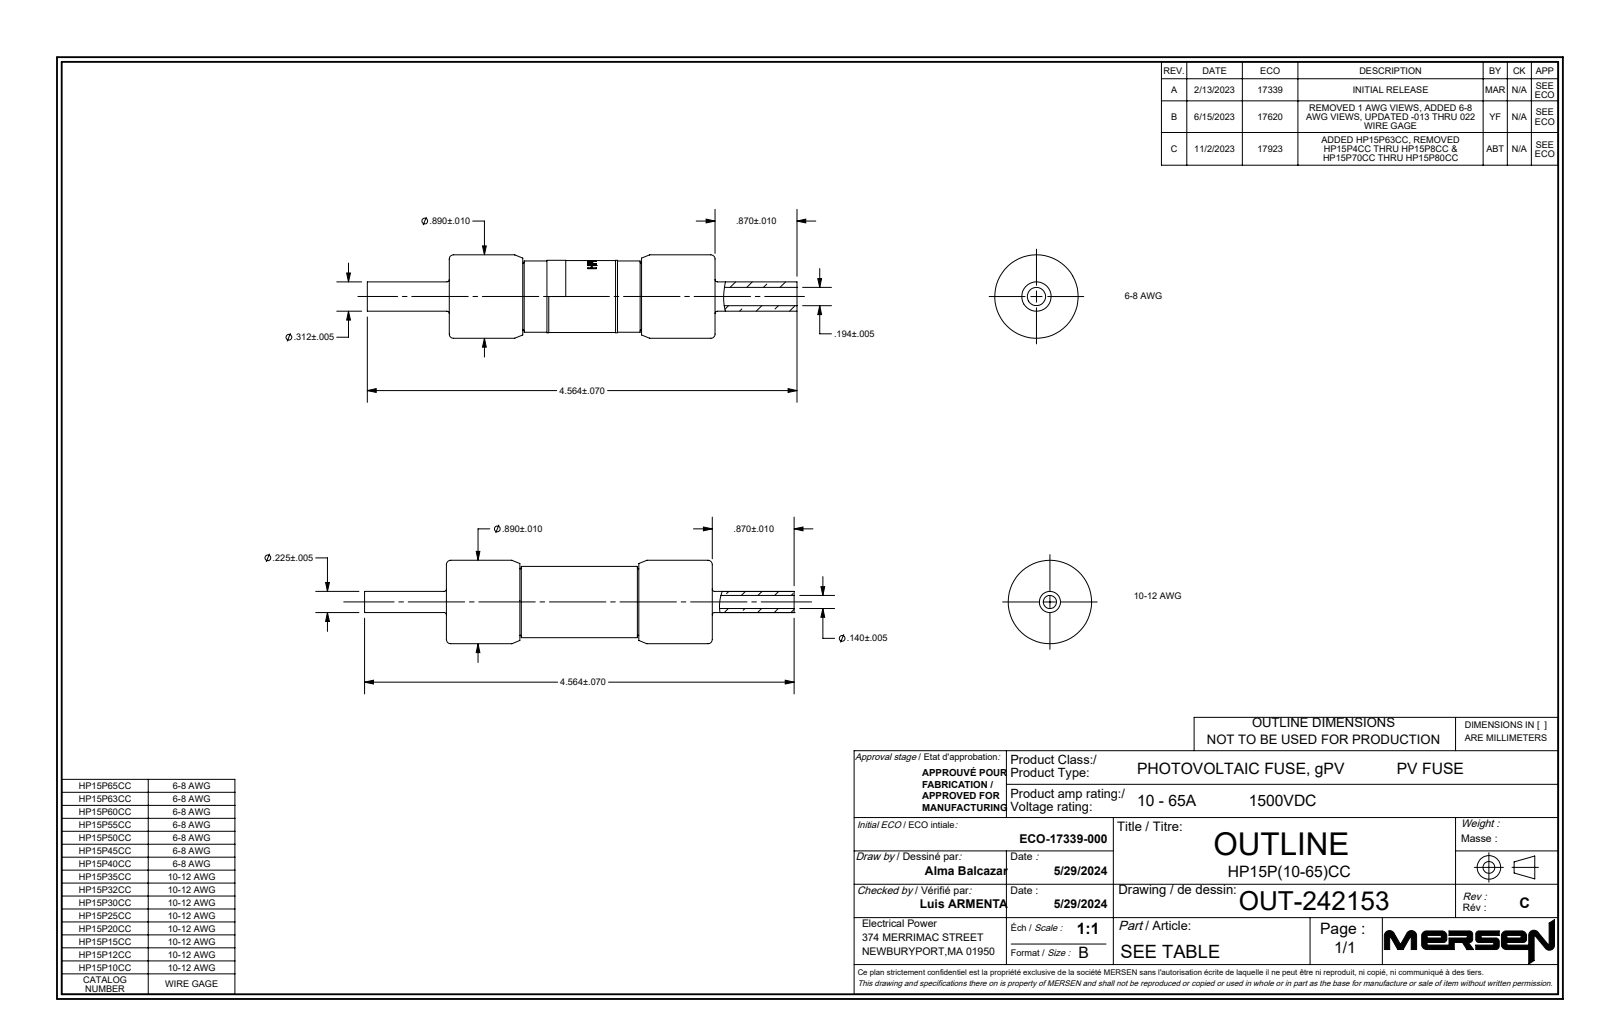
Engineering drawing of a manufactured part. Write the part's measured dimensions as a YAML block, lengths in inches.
part_name: "OUT-242153"
step_written_by: "SolidWorks 2021 (AUTOMOTIVE_DESIGN)"
units: inches
bodies: {solids: 5, faces: 148, planar: 16, cylindrical: 44, other: 88}
overall_size: [4.564, 0.886, 0.886]
volume: 0.887
surface_area: 30.93
round_holes:
  - {diameter: 0.194, count: 1}
  - {diameter: 0.578, count: 1}
  - {diameter: 0.753, count: 1}
  - {diameter: 0.811, count: 1}
round_bosses_or_shafts:
  - {diameter: 0.886, count: 1}
  - {diameter: 0.816, count: 1}
  - {diameter: 0.757, count: 1}
  - {diameter: 0.728, count: 1}
  - {diameter: 0.707, count: 1}
  - {diameter: 0.312, count: 1}
face_to_face_distances: [0.132, 2.692, 0.031, 2.528, 2.56, 2.497, 2.529, 0.032, 2.661, 0.164]
